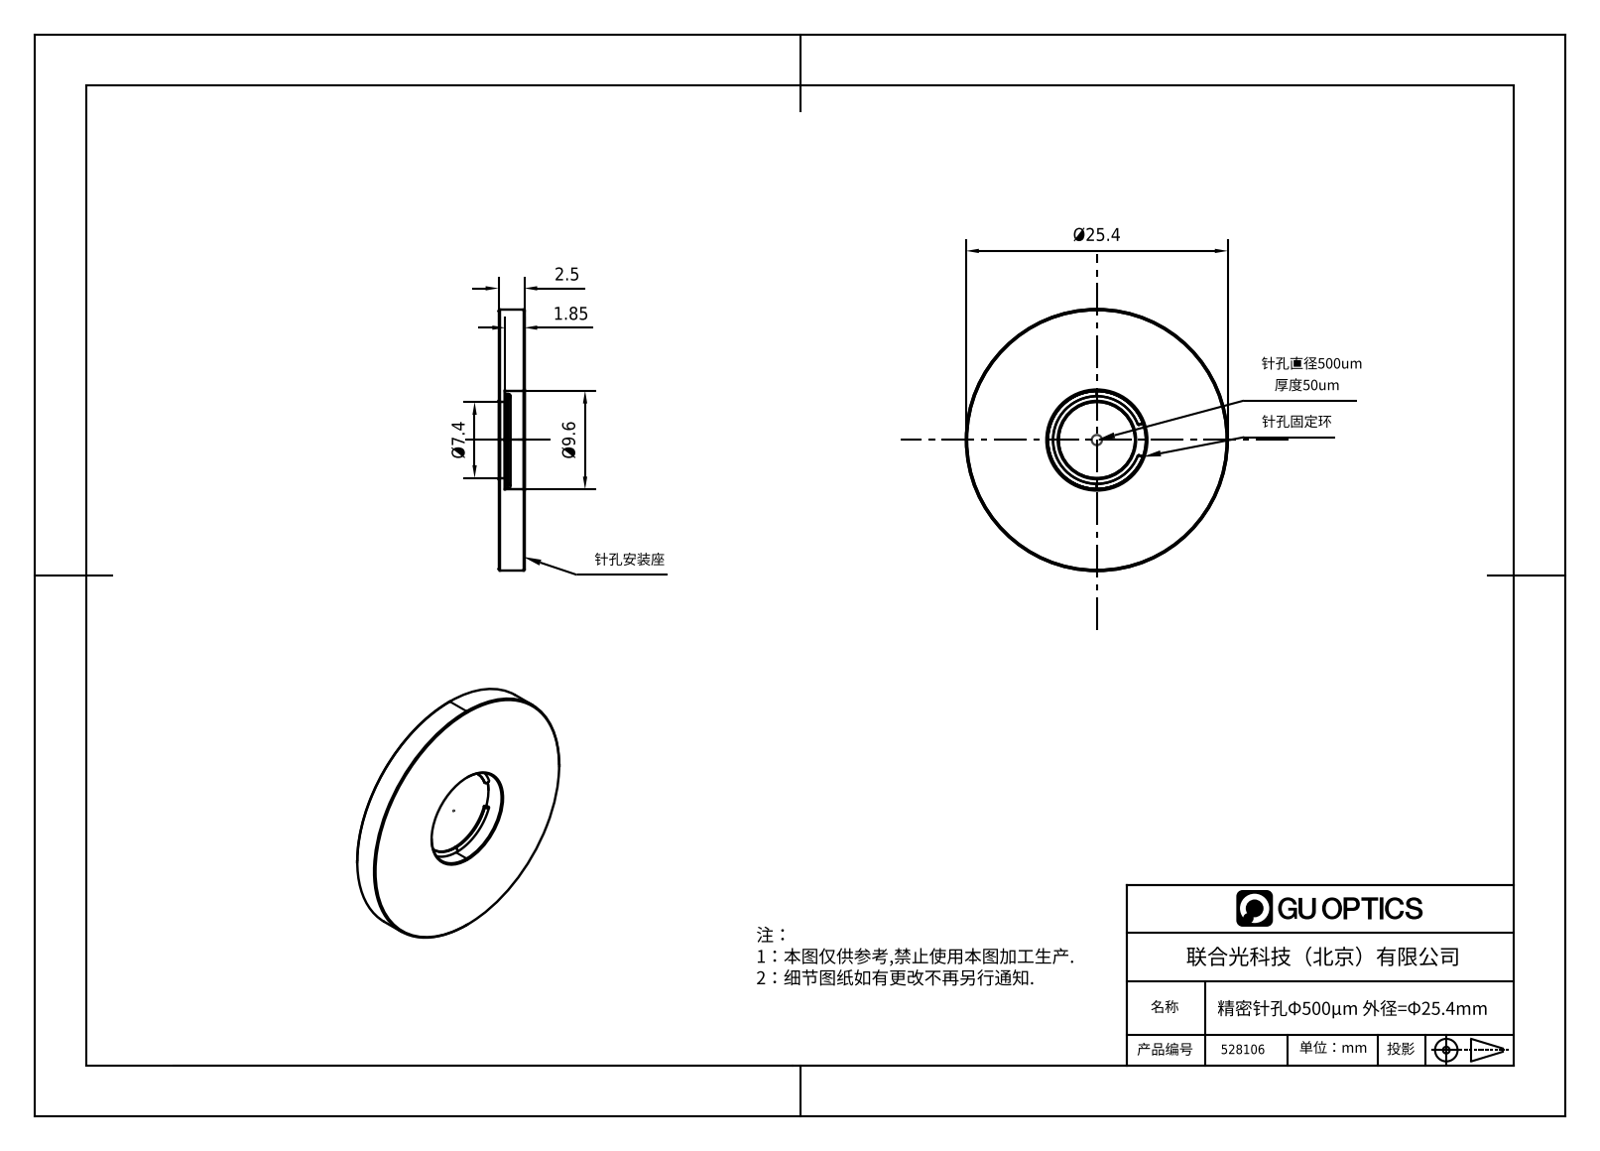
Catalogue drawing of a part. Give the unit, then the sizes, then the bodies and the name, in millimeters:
Units: millimetres
Overall size (bounding box): 25.4 × 25.4 × 2.5
Round holes (diameter × count): ⌀0.5 ×1, ⌀7.4 ×1, ⌀9.6 ×1
Round bosses / shafts (diameter × count): ⌀25.4 ×1
Main face-to-face distances: 2.5, 0.6, 0.65, 1.9, 1.85
Bodies: 0 solids, 28 faces (6 planar, 8 cylindrical, 14 other)
Part name (STEP PRODUCT): 1.5.3.35_ZXO-1.0-500_精密针孔500um，直径25.4（1.0英寸）
STEP written by: SolidWorks 2018 (CONFIG_CONTROL_DESIGN)
